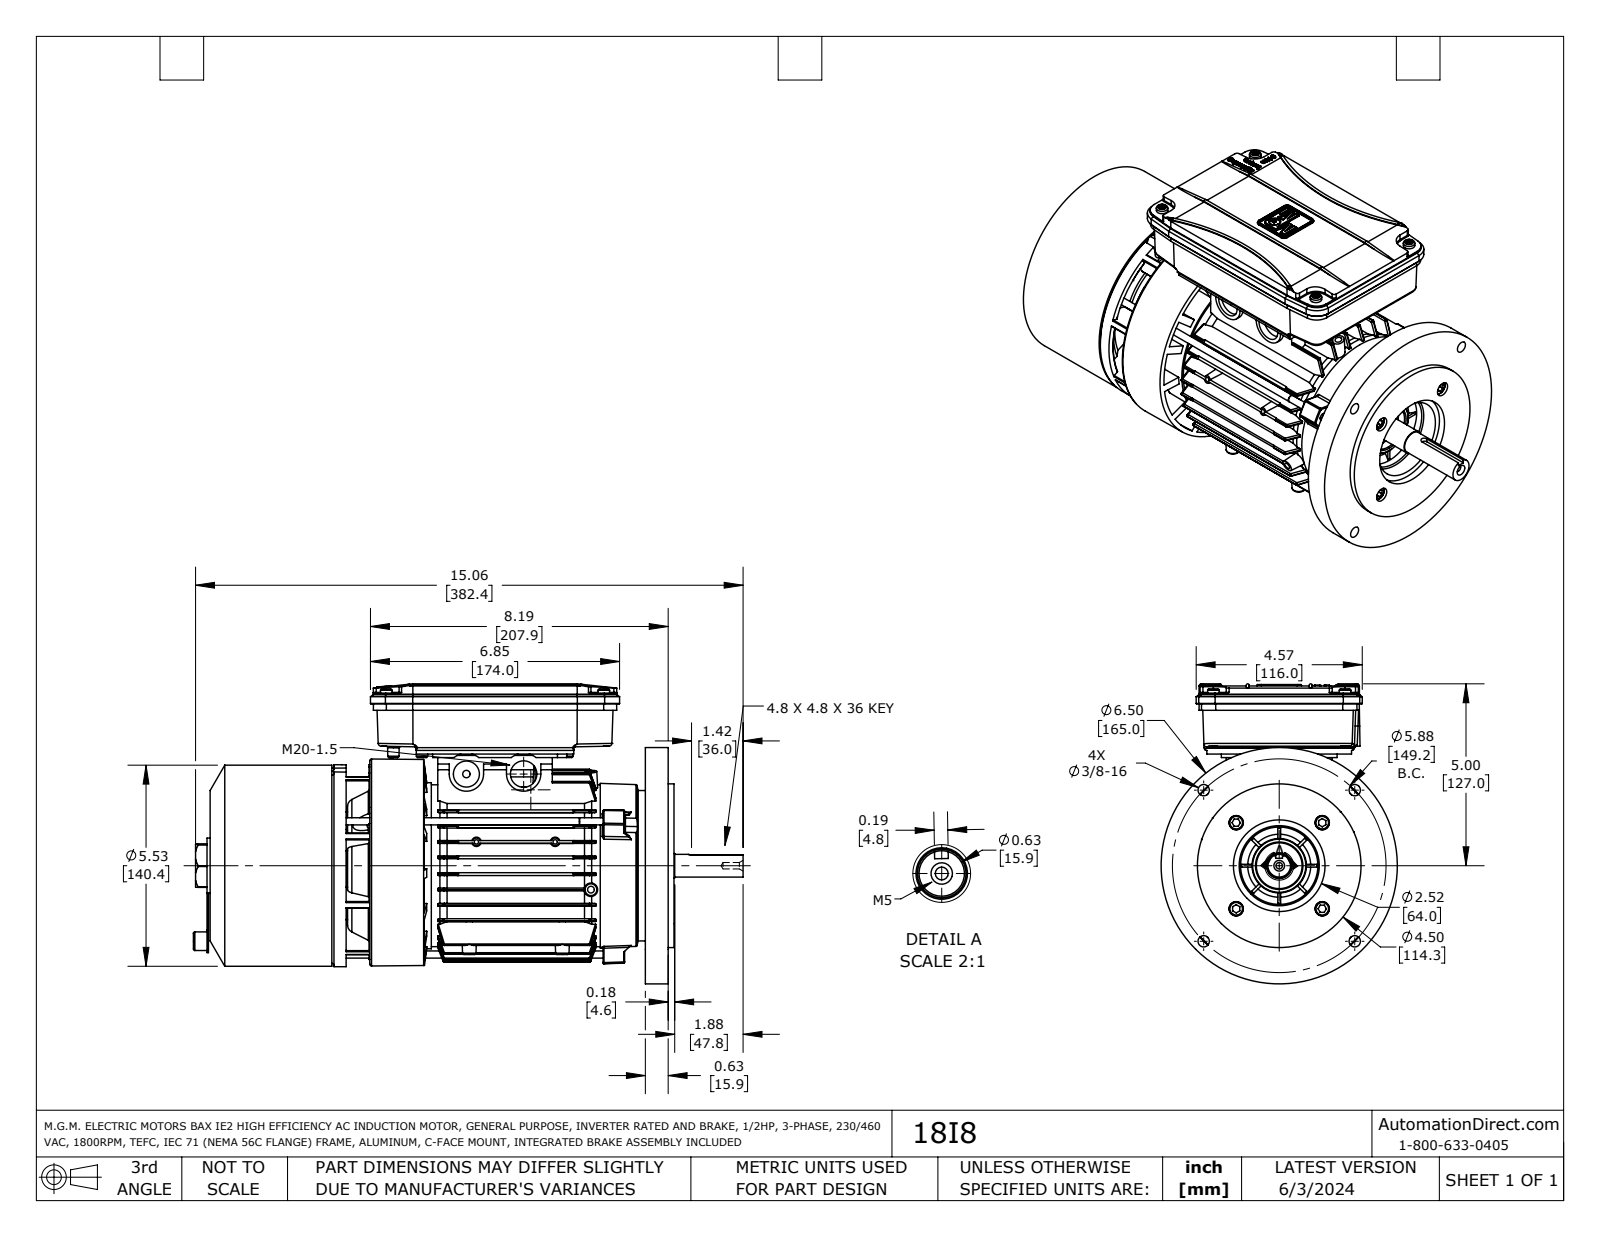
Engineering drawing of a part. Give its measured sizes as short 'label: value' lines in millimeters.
name: 18I8
written by: SolidWorks 2021 (AUTOMOTIVE_DESIGN)
unit: mm
bodies: 25 solids, 3962 faces (1312 planar, 1172 cylindrical, 1478 other)
size: 383.9 × 209.5 × 165
volume: 1 288 000 mm³; area: 750 300 mm²
holes: 21× ⌀3.3, 13× ⌀4.5, 11× ⌀6, 10× ⌀5.5, 8× ⌀4, 7× ⌀2.5, 6× ⌀3, 4× ⌀5, 4× ⌀6.5, 4× ⌀8, 4× ⌀10, 3× ⌀7
bosses: 8× ⌀4.5, 8× ⌀3, 4× ⌀9.8, 4× ⌀8, 4× ⌀6, 3× ⌀5, 1× ⌀165, 1× ⌀141
rounds: 60× R0.9, 56× R0.2, 56× R0.5, 48× R1, 31× R2, 28× R0.6, 24× R0.3, 16× R0.1
face distances: 2, 10.7, 21.4, 43.8, 10, 33.1, 65.3, 8.7, 54.6, 12.7
hole spacings: 12, 85.9, 20.8, 106.8, 53.6, 83.1, 12, 18.9
